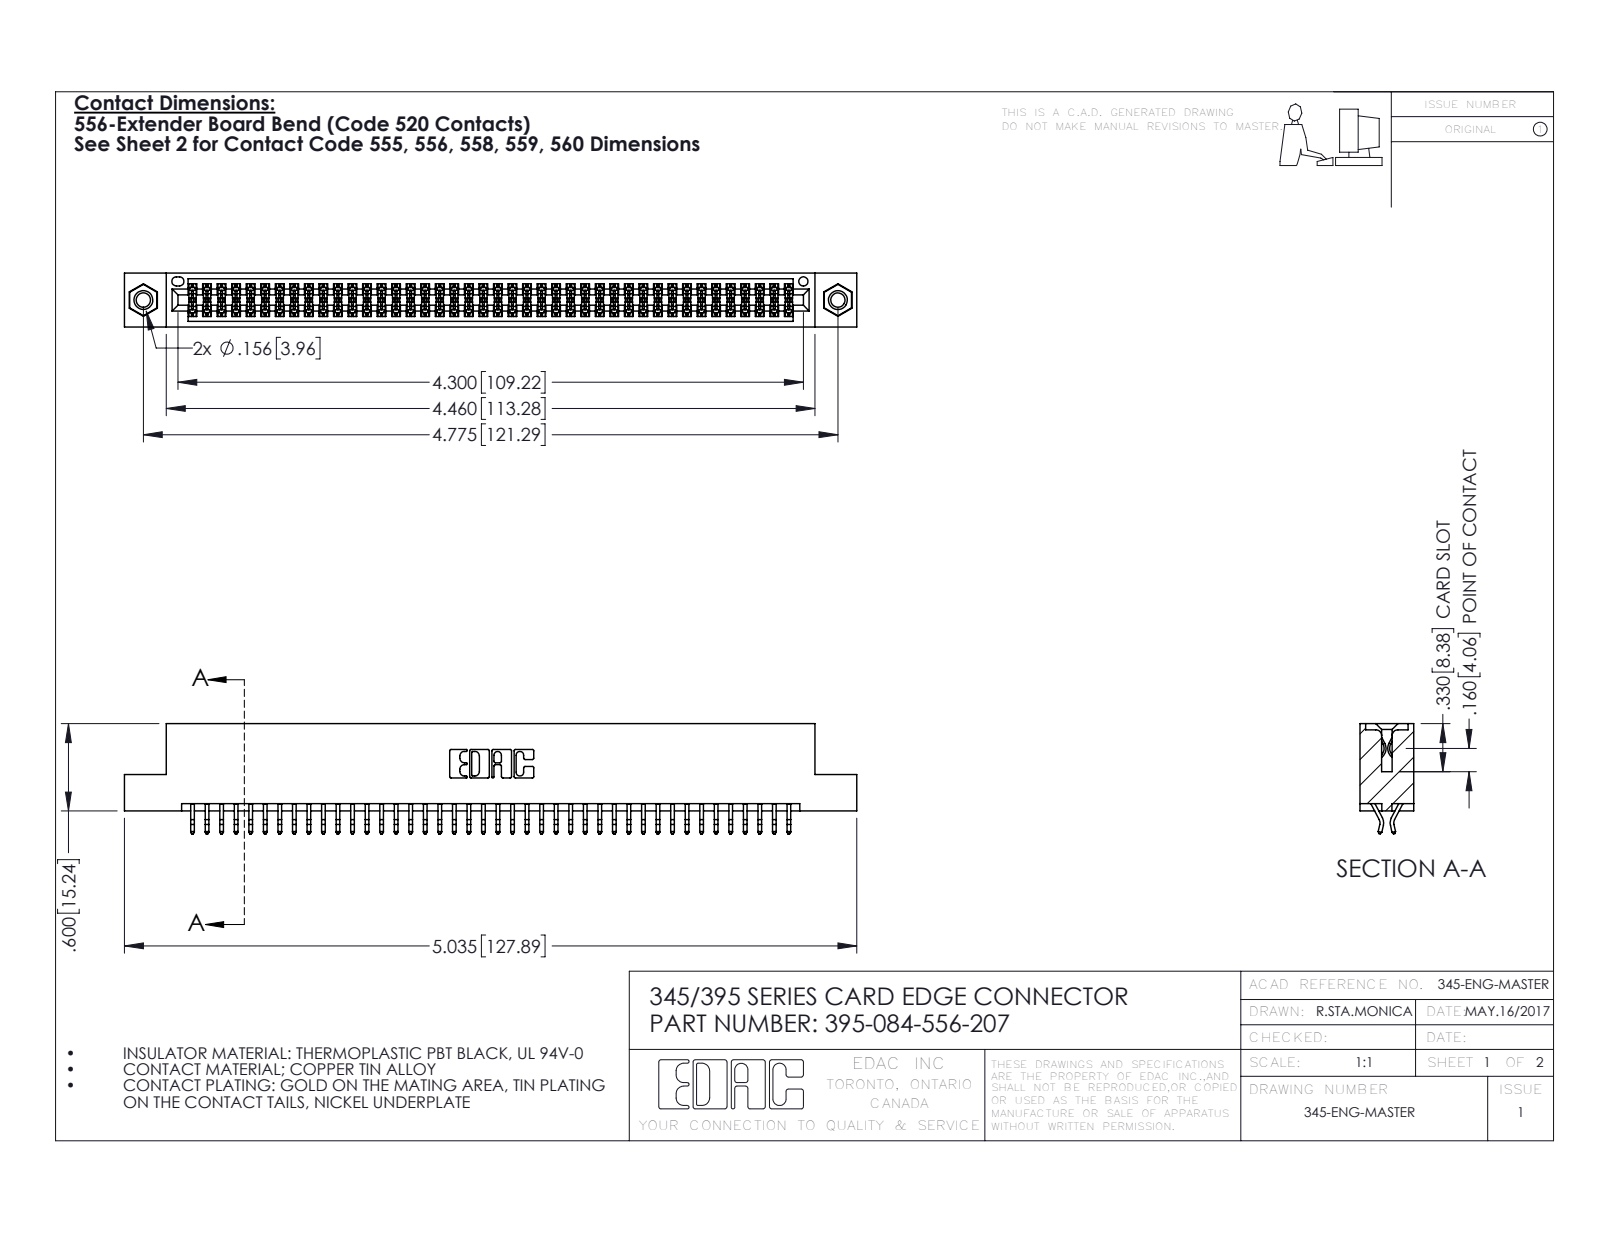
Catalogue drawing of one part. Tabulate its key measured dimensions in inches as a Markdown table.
| quantity | value |
| --- | --- |
| part name | 395-084-556-207; 345-250-001_345-250-005-103; 345-292-001_556 Tail; 345 Part_Flush Mounting Lugs - 0.156 Dia-TI |
| STEP written by | SolidWorks 2016 (CONFIG_CONTROL_DESIGN) |
| units | inches |
| bodies | 87 solids, 4890 faces (3220 planar, 1654 cylindrical, 16 other) |
| overall size | 5.035 × 0.757 × 0.37 |
| volume | 0.757 in³ |
| surface area | 28.35 in² |
| round holes (diameter × count) | 0.098 × 2, 0.125 × 2, 0.156 × 2, 0.064 × 1 |
| round bosses / shafts (diameter × count) | 0.155 × 2 |
| partial cylindrical surfaces (radius × count) | 0.006 × 126, 0.01 × 22, 0.007 × 6, 0.031 × 6, 0.026 × 3, 0.01 × 2, 0.014 × 2, 0.019 × 2 |
| main face-to-face distances | 0.072, 0.298, 0.2, 0.37, 0.025, 0.098, 0.272, 0.225, 0.175, 0.149 |
| hole center spacings | 0.27, 4.539, 4.775 |
